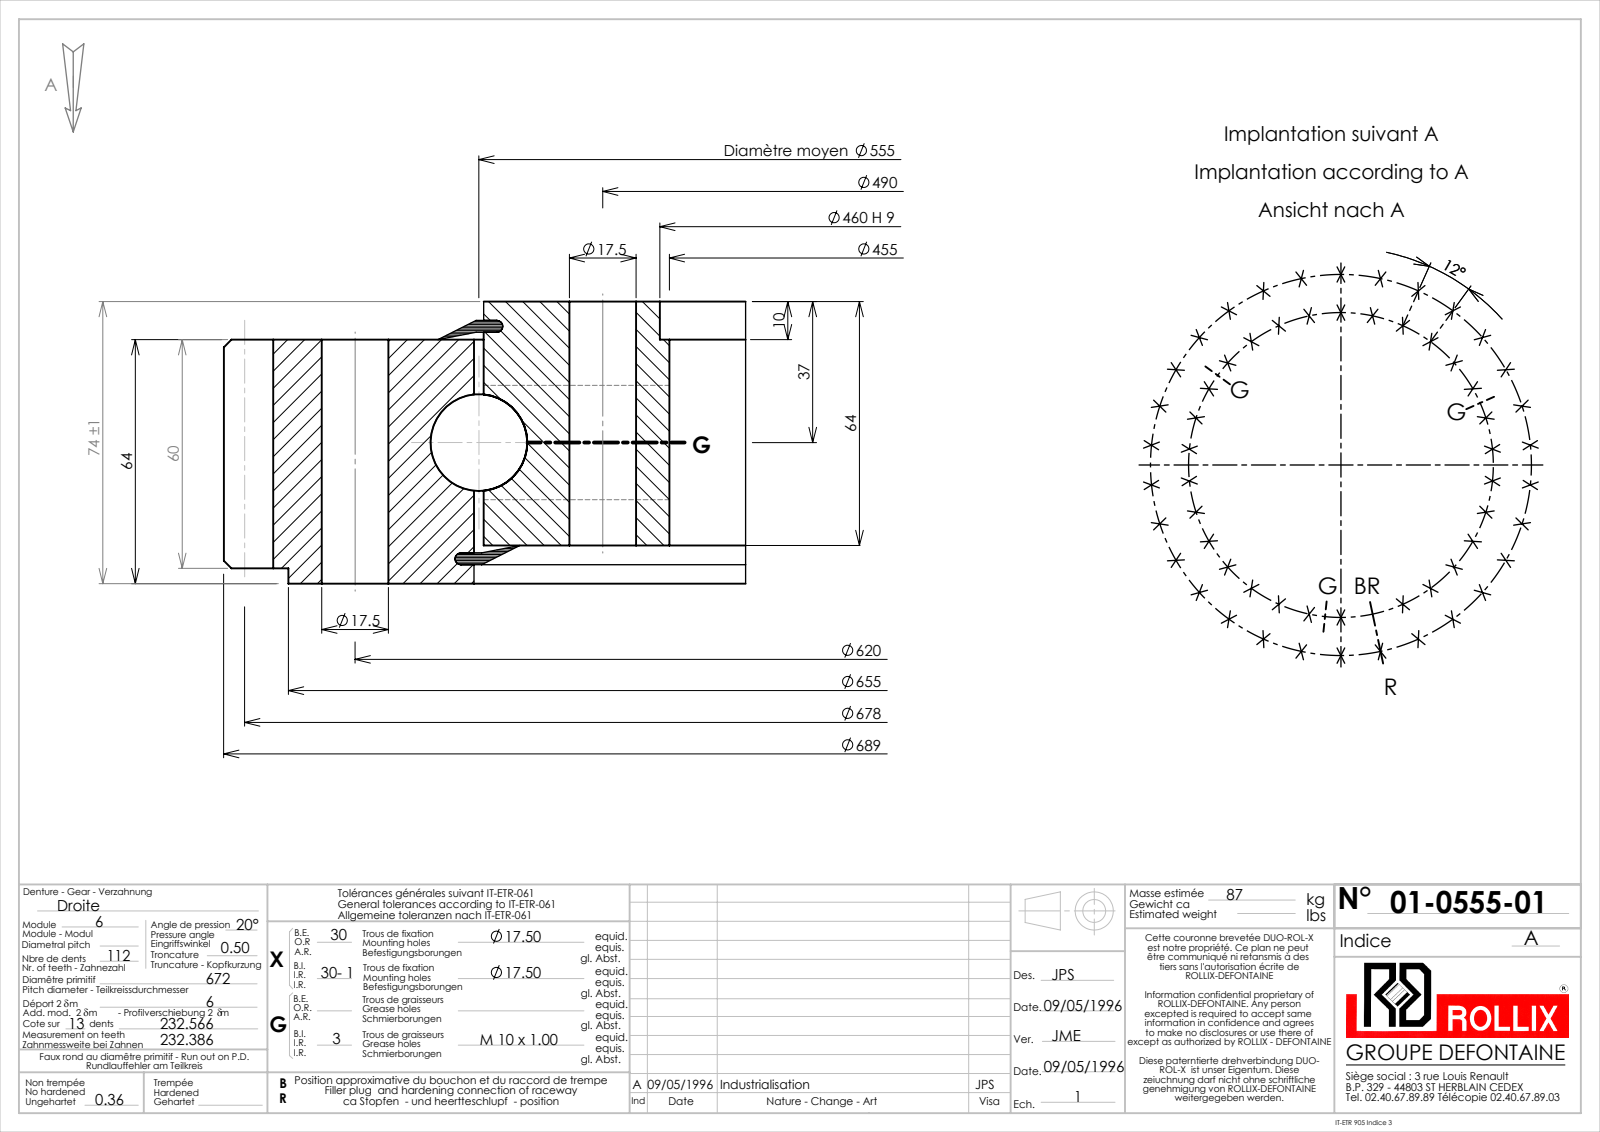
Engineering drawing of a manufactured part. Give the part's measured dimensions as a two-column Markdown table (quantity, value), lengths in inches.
| quantity | value |
| --- | --- |
| part name | 01-0555-01 |
| STEP written by | SolidWorks 2016 (CONFIG_CONTROL_DESIGN) |
| units | inches |
| bodies | 5 solids, 857 faces (238 planar, 367 cylindrical, 252 other) |
| overall size | 27.121 × 27.121 × 2.913 |
| volume | 648.1 in³ |
| surface area | 2 083 in² |
| round holes (diameter × count) | 0.689 × 59, 0.354 × 3, 17.913 × 1, 18.11 × 1, 21.95 × 1 |
| round bosses / shafts (diameter × count) | 25.787 × 1, 21.75 × 1 |
| partial cylindrical surfaces (radius × count) | 13.051 × 1, 13.563 × 1 |
| main face-to-face distances | 2.52, 0.394, 2.126, 2.913, 0.317, 2.596, 0.077, 2.203, 0.195, 2.719 |
| hole center spacings | 7.543, 18.14, 23.876, 12.205, 23.215, 19.748, 16.333, 21.139 |
